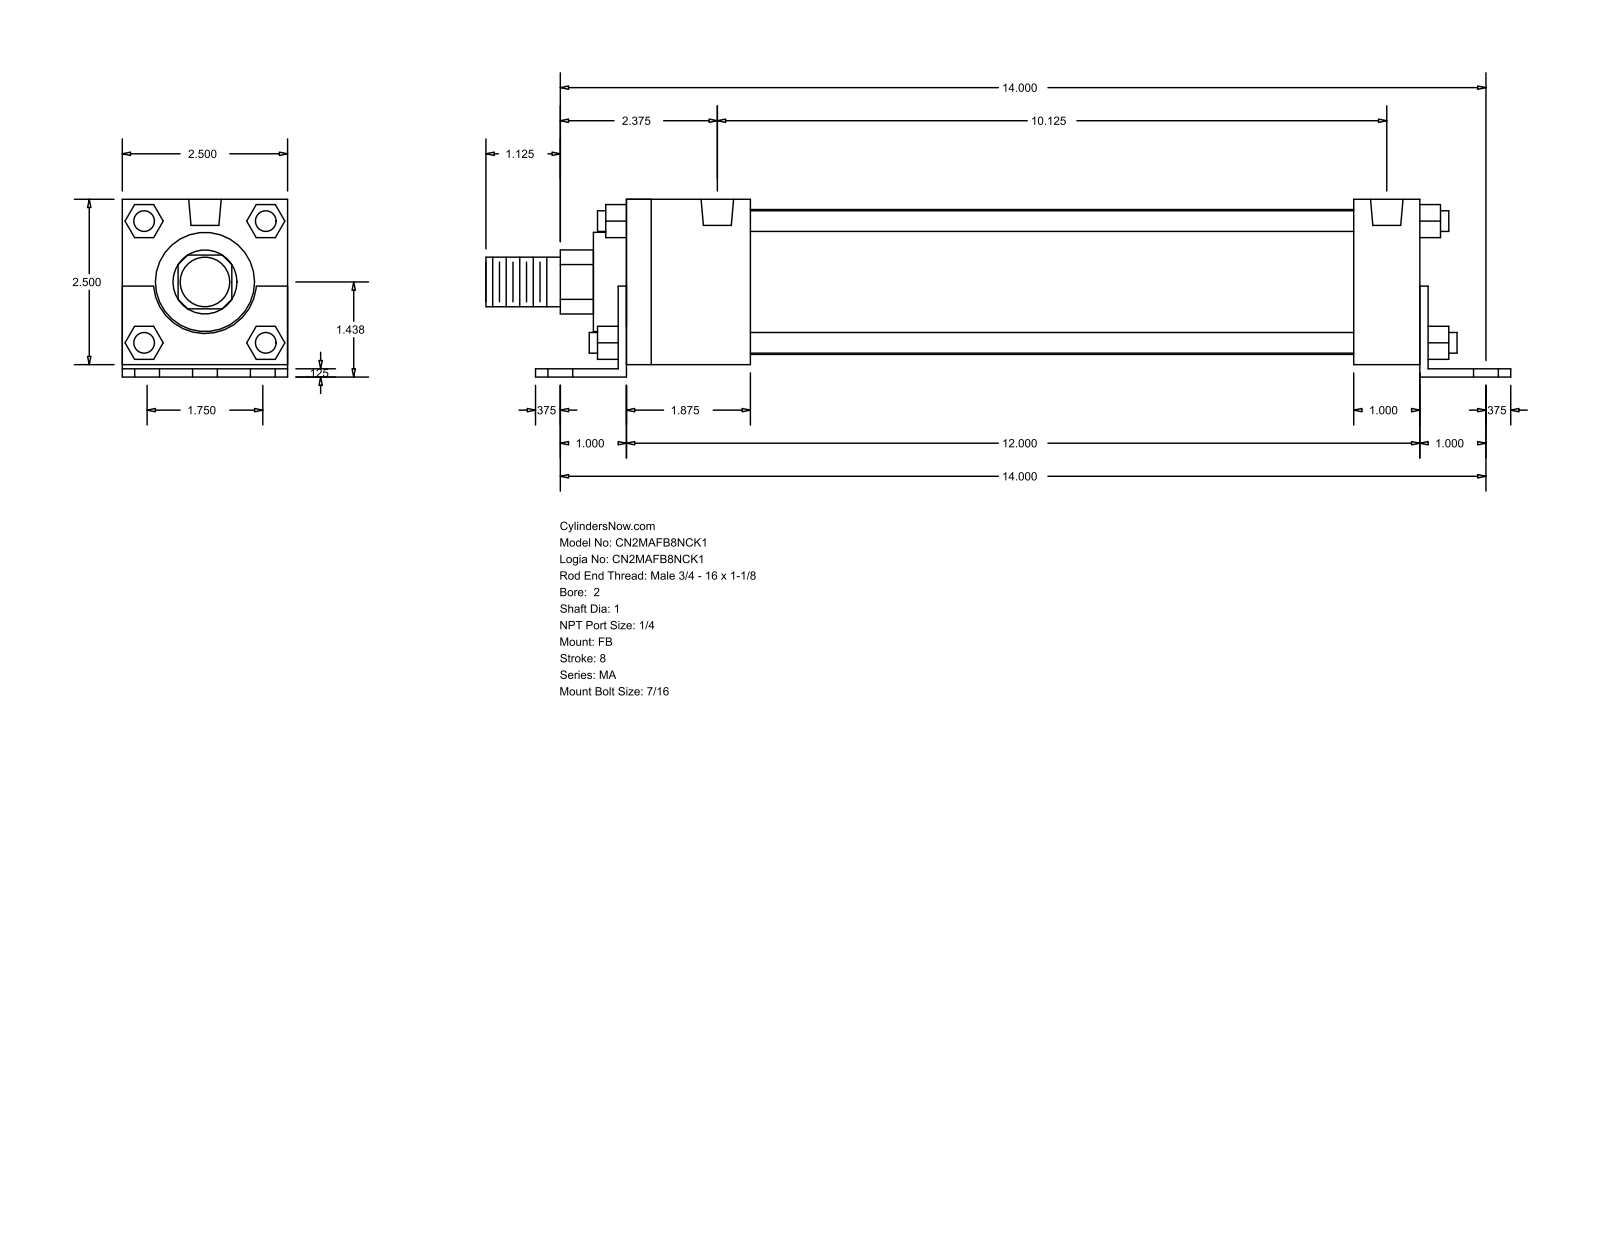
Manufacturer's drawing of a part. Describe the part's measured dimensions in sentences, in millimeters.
The part is named "MA_FB__0200_1". Its 3-D file was written by "GSSL Pune (CONFIG_CONTROL_DESIGN)". It is 0 solids with 140 faces: 105 planar, 35 cylindrical and 0 other. Overall it measures 393.7 by 68.26 by 63.5 millimeters. Round holes: 6 of diameter 11.11, 4 of diameter 7.94, 2 of diameter 12.49. Round bosses or shafts: 4 of diameter 7.94, 1 of diameter 55.63, 1 of diameter 38.1, 1 of diameter 25.4, 1 of diameter 19.05. Partial cylindrical surfaces (rounded edges, fillets, slot ends): 1 of radius 12.29, 1 of radius 19.81. The main face-to-face distances are 63.5, 3.17, 4.76, 68.26, 1.59, 65.09, 12.7, 3.18, 304.8, 307.98. The hole center spacings are 22.23, 356.29, 355.6, 44.11, 44.46, 64.3, 257.17, 296.11.
